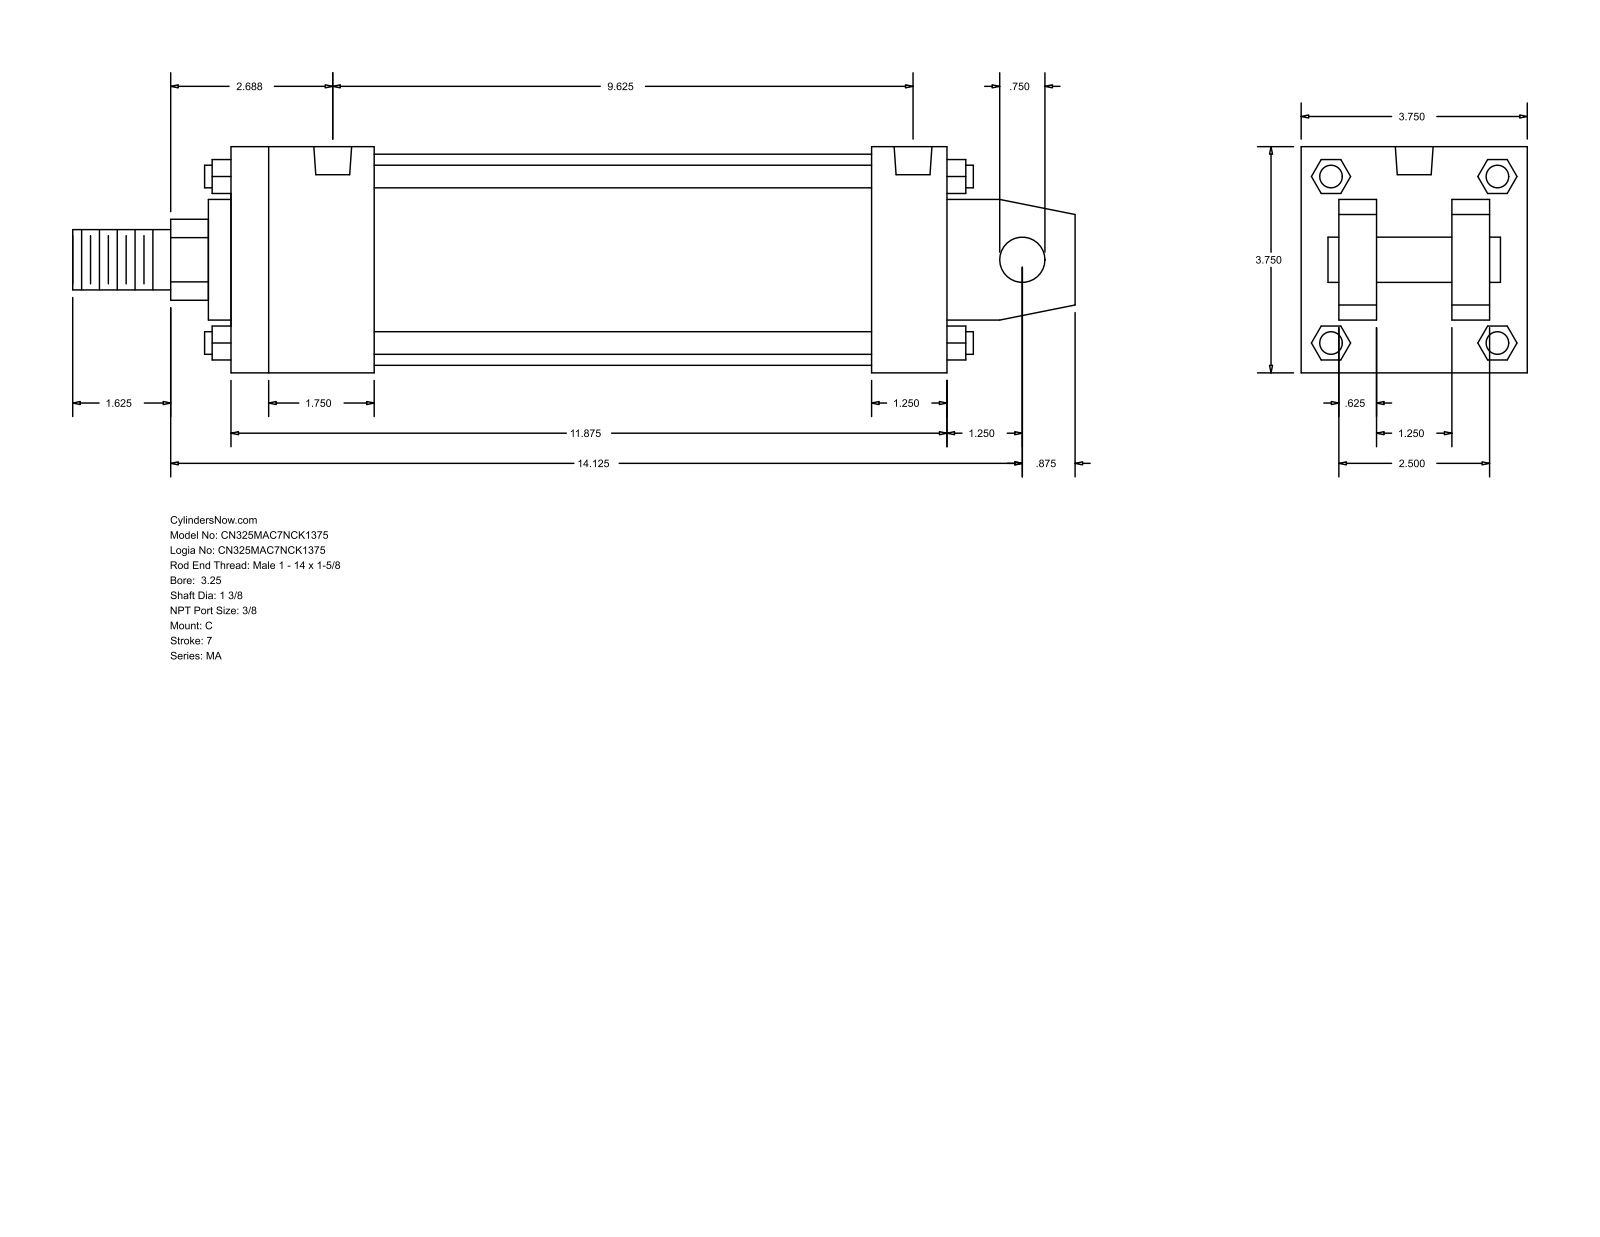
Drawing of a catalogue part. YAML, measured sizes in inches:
part_name: "MA_C__0325_1.375"
step_written_by: "GSSL Pune (CONFIG_CONTROL_DESIGN)"
units: inches
bodies: {solids: 0, faces: 139, planar: 108, cylindrical: 31, other: 0}
overall_size: [16.625, 3.75, 3.75]
round_holes:
  - {diameter: 0.437, count: 4}
  - {diameter: 0.627, count: 2}
round_bosses_or_shafts:
  - {diameter: 0.375, count: 4}
  - {diameter: 3.5, count: 1}
  - {diameter: 2, count: 1}
  - {diameter: 1.375, count: 1}
  - {diameter: 1, count: 1}
  - {diameter: 0.75, count: 1}
partial_cylinders:
  - {radius: 0.672, count: 1}
face_to_face_distances: [3.75, 0.625, 2.5, 11.875, 1.25, 3.125, 1.875, 10.625, 1.25, 2.375]
hole_center_spacings: [9.25, 0.187, 0.188, 9.437, 9.438, 9.625]
